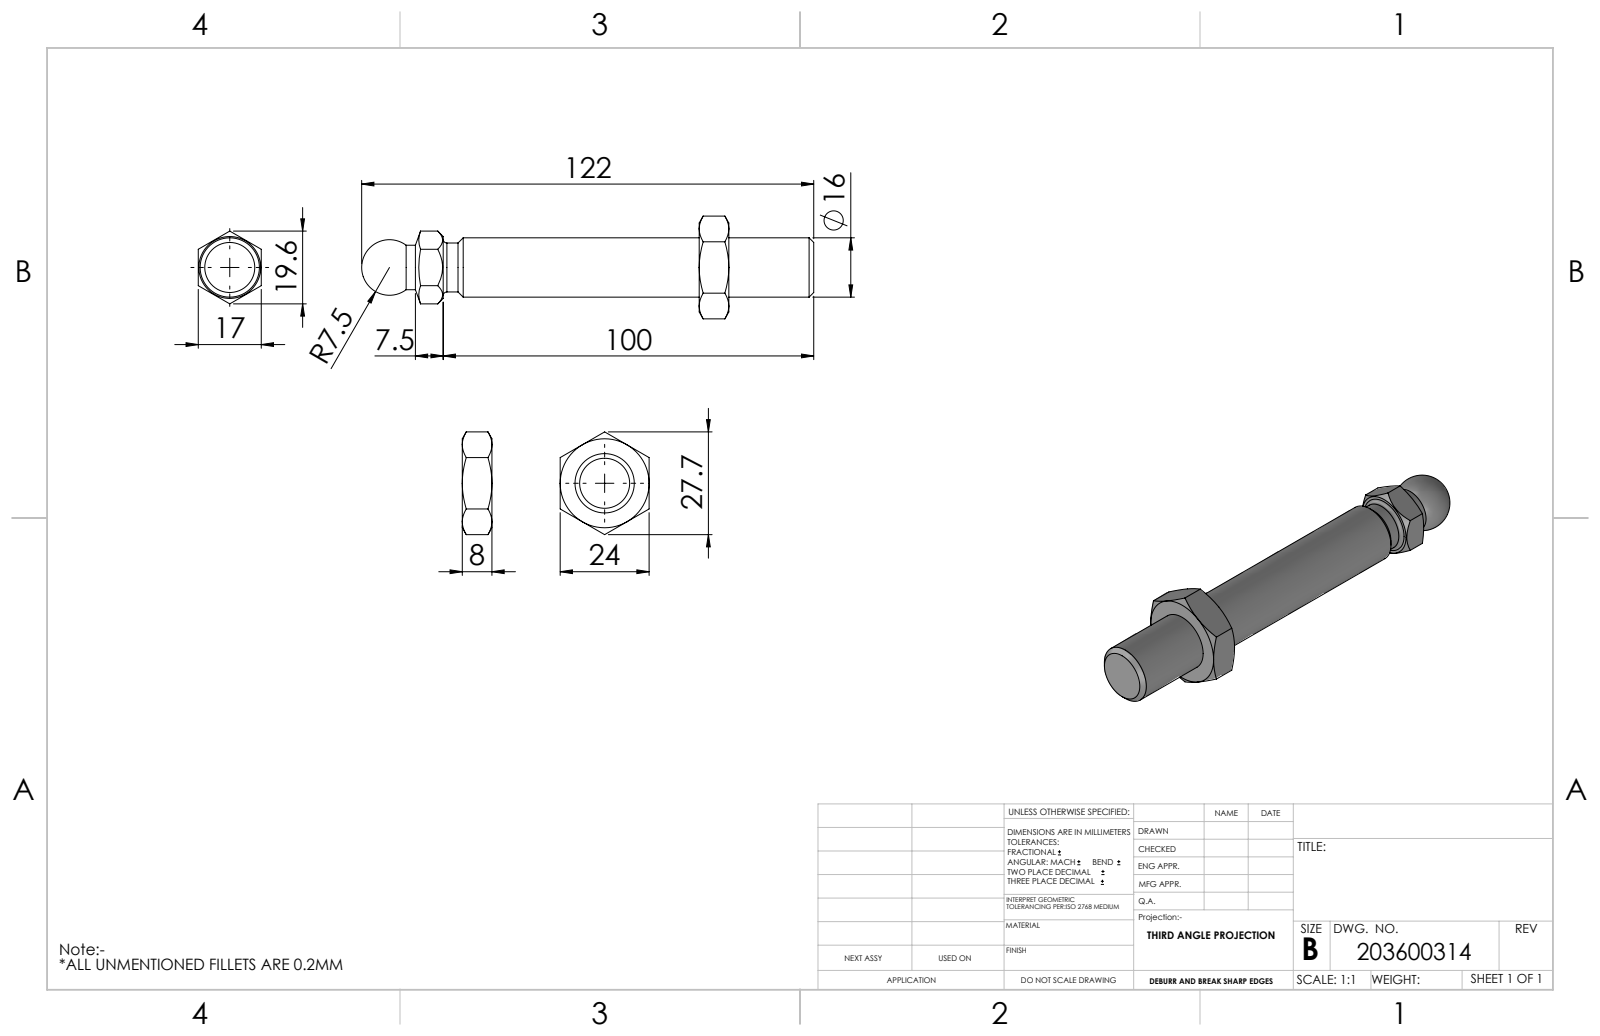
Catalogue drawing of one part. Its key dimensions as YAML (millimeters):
part_name: "203600314_c_1"
step_written_by: "SolidWorks 2014 (CONFIG_CONTROL_DESIGN)"
units: millimeters
bodies: {solids: 2, faces: 60, planar: 16, cylindrical: 10, other: 34}
overall_size: [122, 27.71, 24]
volume: 26120
surface_area: 8052
round_holes:
  - {diameter: 14, count: 1}
  - {diameter: 16, count: 1}
round_bosses_or_shafts:
  - {diameter: 13.2, count: 1}
  - {diameter: 12, count: 1}
face_to_face_distances: [3.5, 20.5, 24, 8, 17, 30.91, 22.91, 69.09, 77.09, 100]
